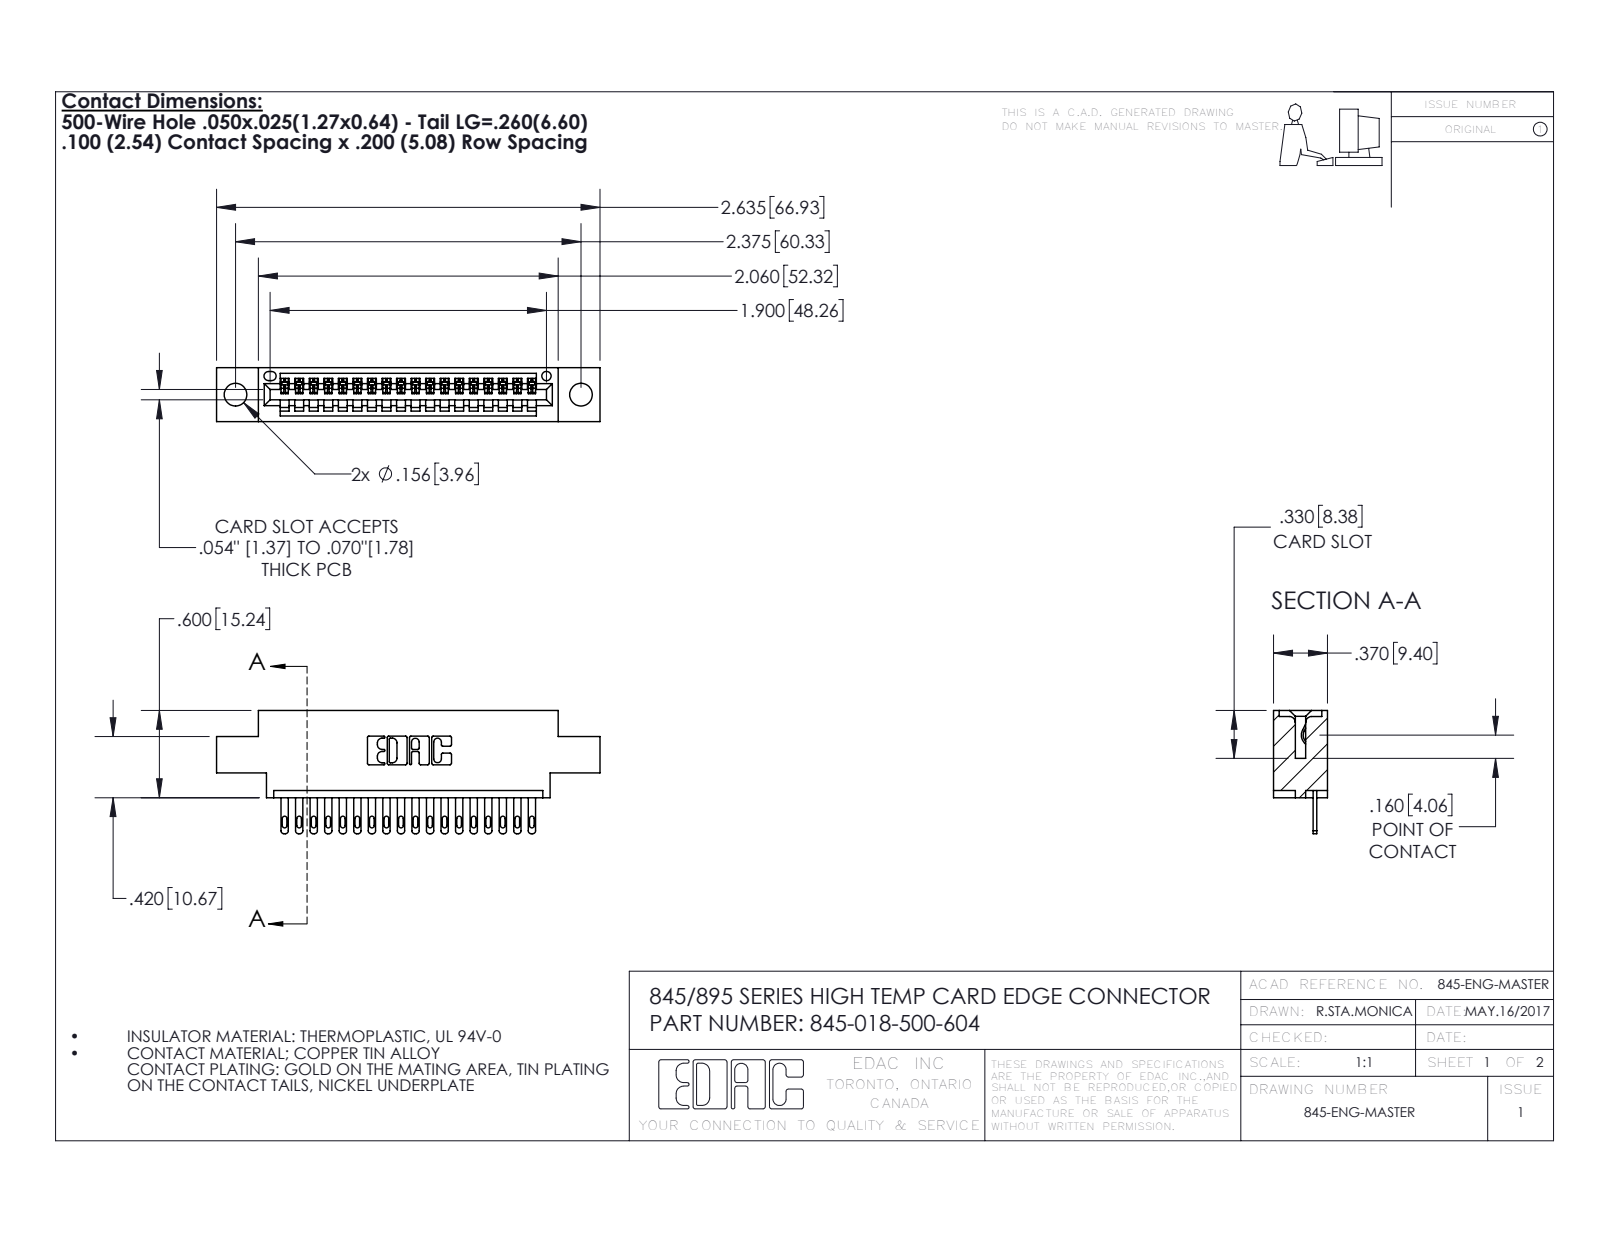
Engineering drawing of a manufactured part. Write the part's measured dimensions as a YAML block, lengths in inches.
part_name: "345-292-001_345-293-100; 345 Part_0.170 Offset - 0.156 Dia-TH; 345-018-500-604"
step_written_by: "SolidWorks 2016 (CONFIG_CONTROL_DESIGN)"
units: inches
bodies: {solids: 19, faces: 1102, planar: 696, cylindrical: 406, other: 0}
overall_size: [2.635, 2.066, 0.37]
volume: 0.366
surface_area: 11.56
round_holes:
  - {diameter: 0.156, count: 2}
  - {diameter: 0.064, count: 1}
partial_cylinders:
  - {radius: 0.006, count: 36}
  - {radius: 0.016, count: 36}
  - {radius: 0.02, count: 36}
  - {radius: 0.01, count: 22}
  - {radius: 0.007, count: 6}
  - {radius: 0.031, count: 6}
  - {radius: 0.026, count: 3}
  - {radius: 0.031, count: 2}
face_to_face_distances: [0.298, 0.072, 0.37, 0.2, 0.098, 0.272, 0.025, 0.225, 0.1, 0.15]
hole_center_spacings: [0.27, 2.141, 2.375]
